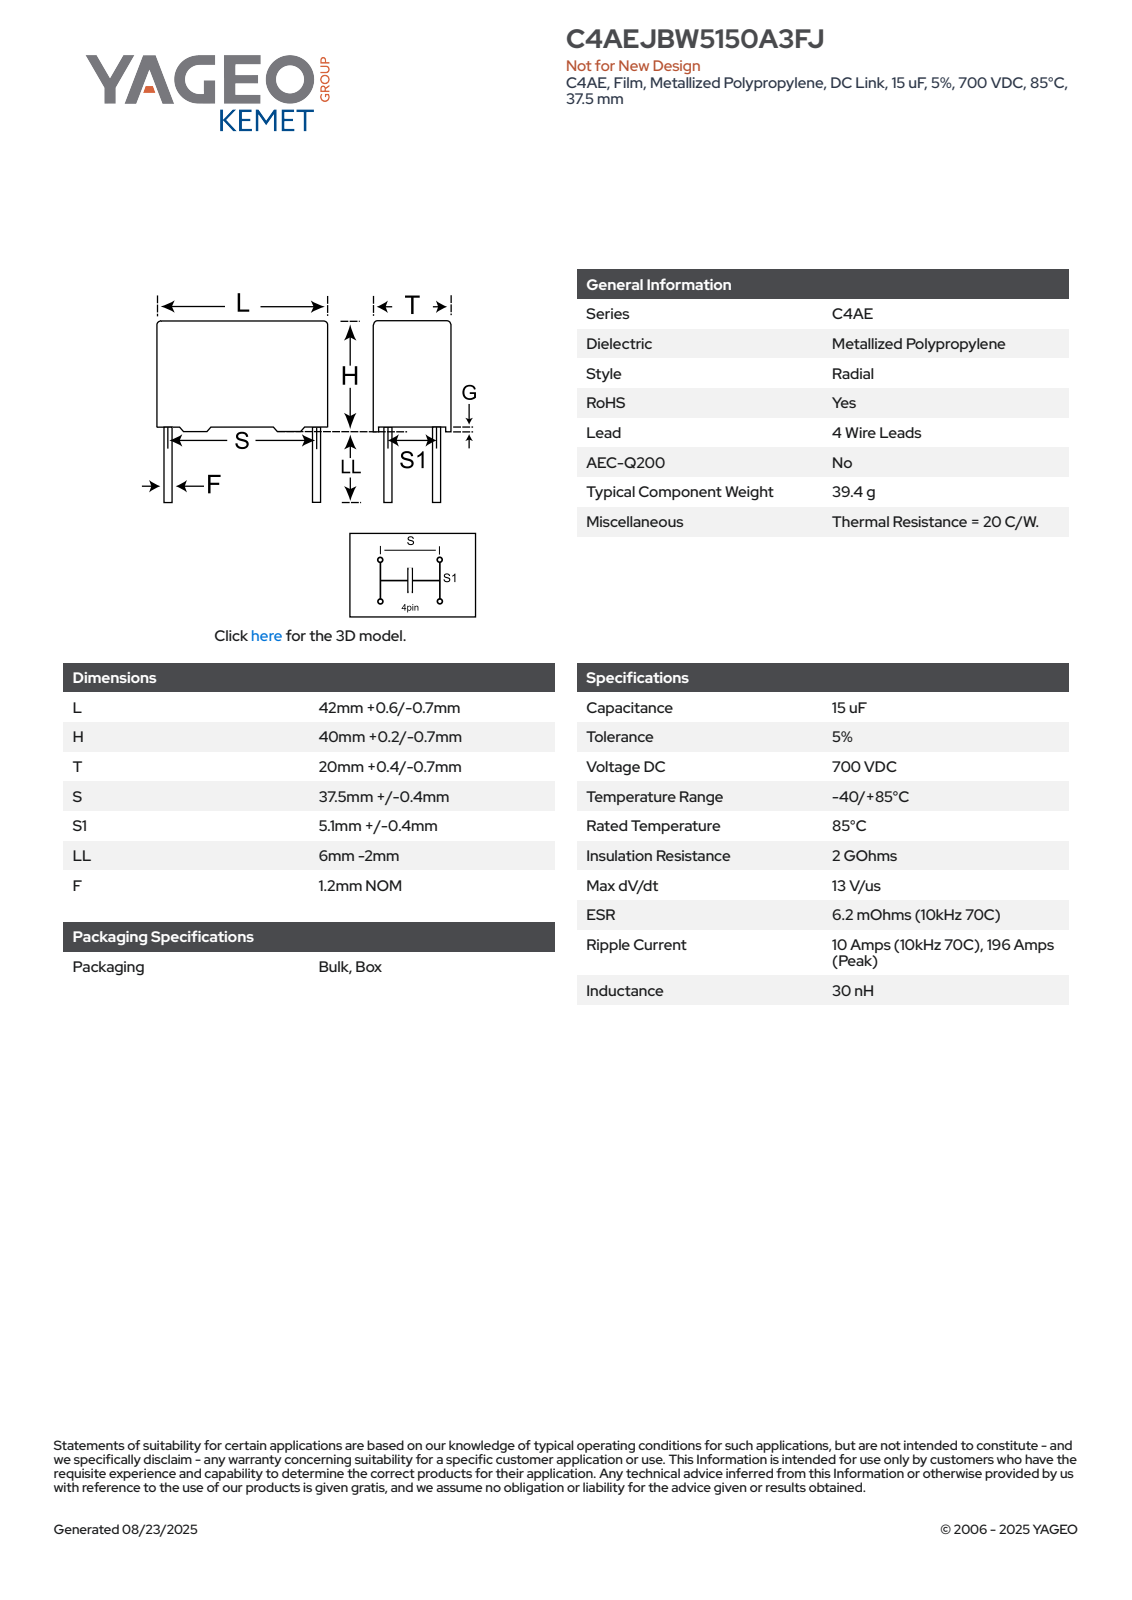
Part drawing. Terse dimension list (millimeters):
name: CFP_RB4G_42X40X20_L42.6H40.2T20.4S37.5S15.1LL4F1.2G0.5
written by: SolidWorks 2014 (AUTOMOTIVE_DESIGN)
unit: mm
bodies: 4 solids, 91 faces (83 planar, 8 cylindrical, 0 other)
size: 44.2 × 42.6 × 20.41
volume: 34 548 mm³; area: 6 920 mm²
bosses: 4× ⌀1.2
face distances: 20.4, 42.6, 39.7, 0.5, 40.2, 18.4, 2, 16.4, 16.84, 4
